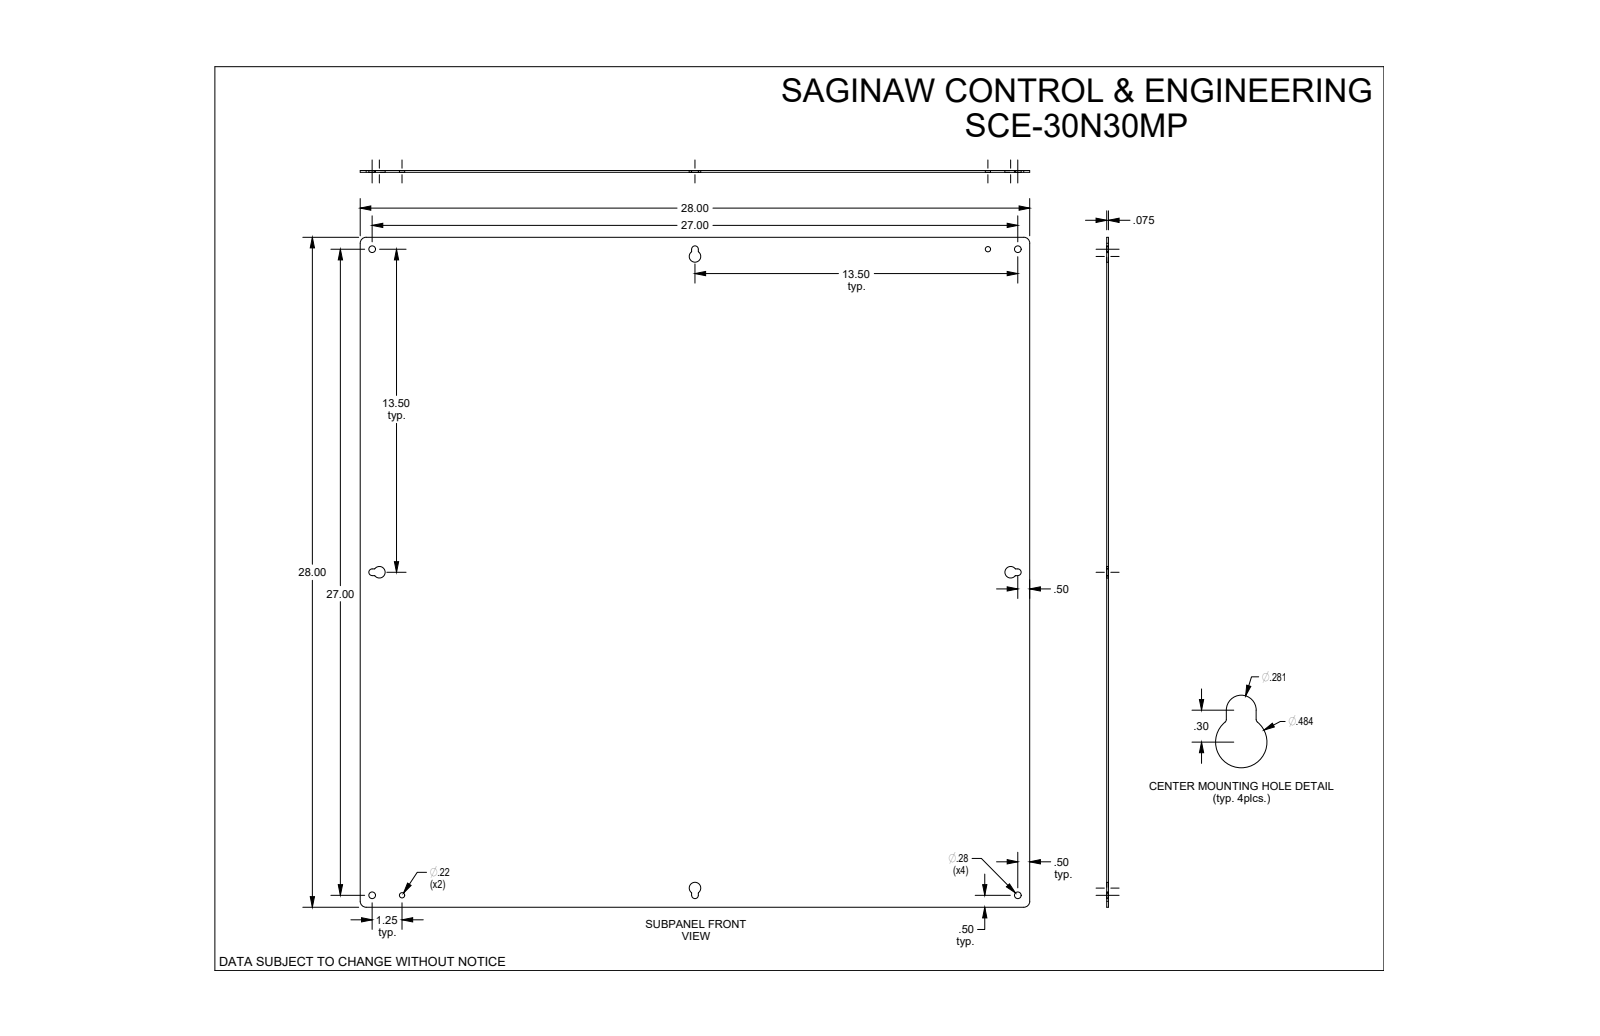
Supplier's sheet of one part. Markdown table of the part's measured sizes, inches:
| quantity | value |
| --- | --- |
| part name | SCE-30N30MP |
| STEP written by | SolidWorks 2019 (CONFIG_CONTROL_DESIGN) |
| units | inches |
| bodies | 1 solid, 40 faces (14 planar, 26 cylindrical, 0 other) |
| overall size | 28 × 28 × 0.075 |
| volume | 58.7 in³ |
| surface area | 1 575 in² |
| round holes (diameter × count) | 0.281 × 4, 0.218 × 2 |
| partial cylindrical surfaces (radius × count) | 0.03 × 8, 0.141 × 4, 0.242 × 4, 0.25 × 4 |
| main face-to-face distances | 0.075, 28, 13.859, 14.141, 0.281 |
| hole center spacings | 27, 1.25, 25.75, 27.029, 37.31, 38.184, 36.459 |
